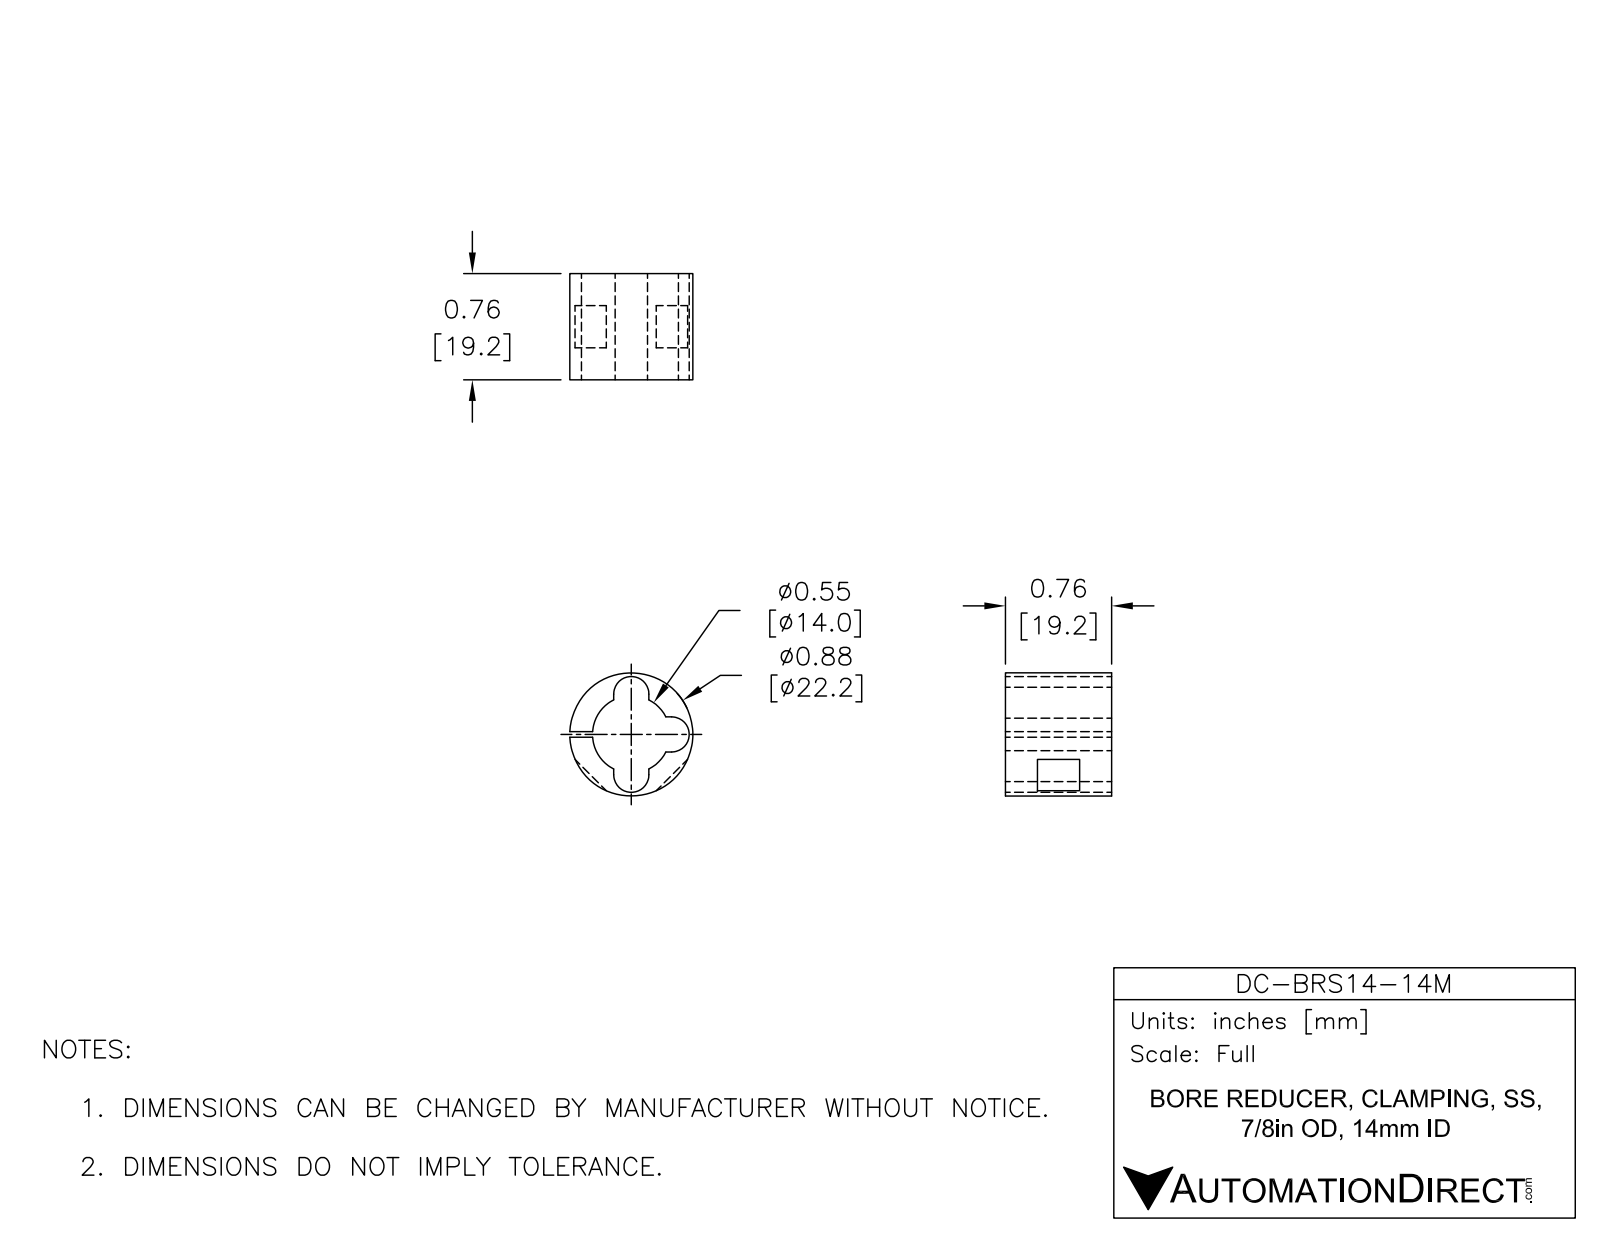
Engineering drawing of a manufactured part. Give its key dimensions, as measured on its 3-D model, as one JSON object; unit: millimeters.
{"part_name": "DC-BRS14-14M", "step_written_by": "SolidWorks 2015 (AUTOMOTIVE_DESIGN)", "units": "millimeters", "bodies": {"solids": 1, "faces": 27, "planar": 16, "cylindrical": 11, "other": 0}, "overall_size": [22.23, 22.21, 19.18], "volume_mm3": 3245, "surface_area_mm2": 2973, "round_bosses_or_shafts": [[22.22, 1]], "partial_cylinders_radius": [[3.17, 3], [7, 1]], "face_to_face_distances": [19.18, 1.02, 6.34, 2.66, 3.68, 5.78, 13.4, 7.62]}
